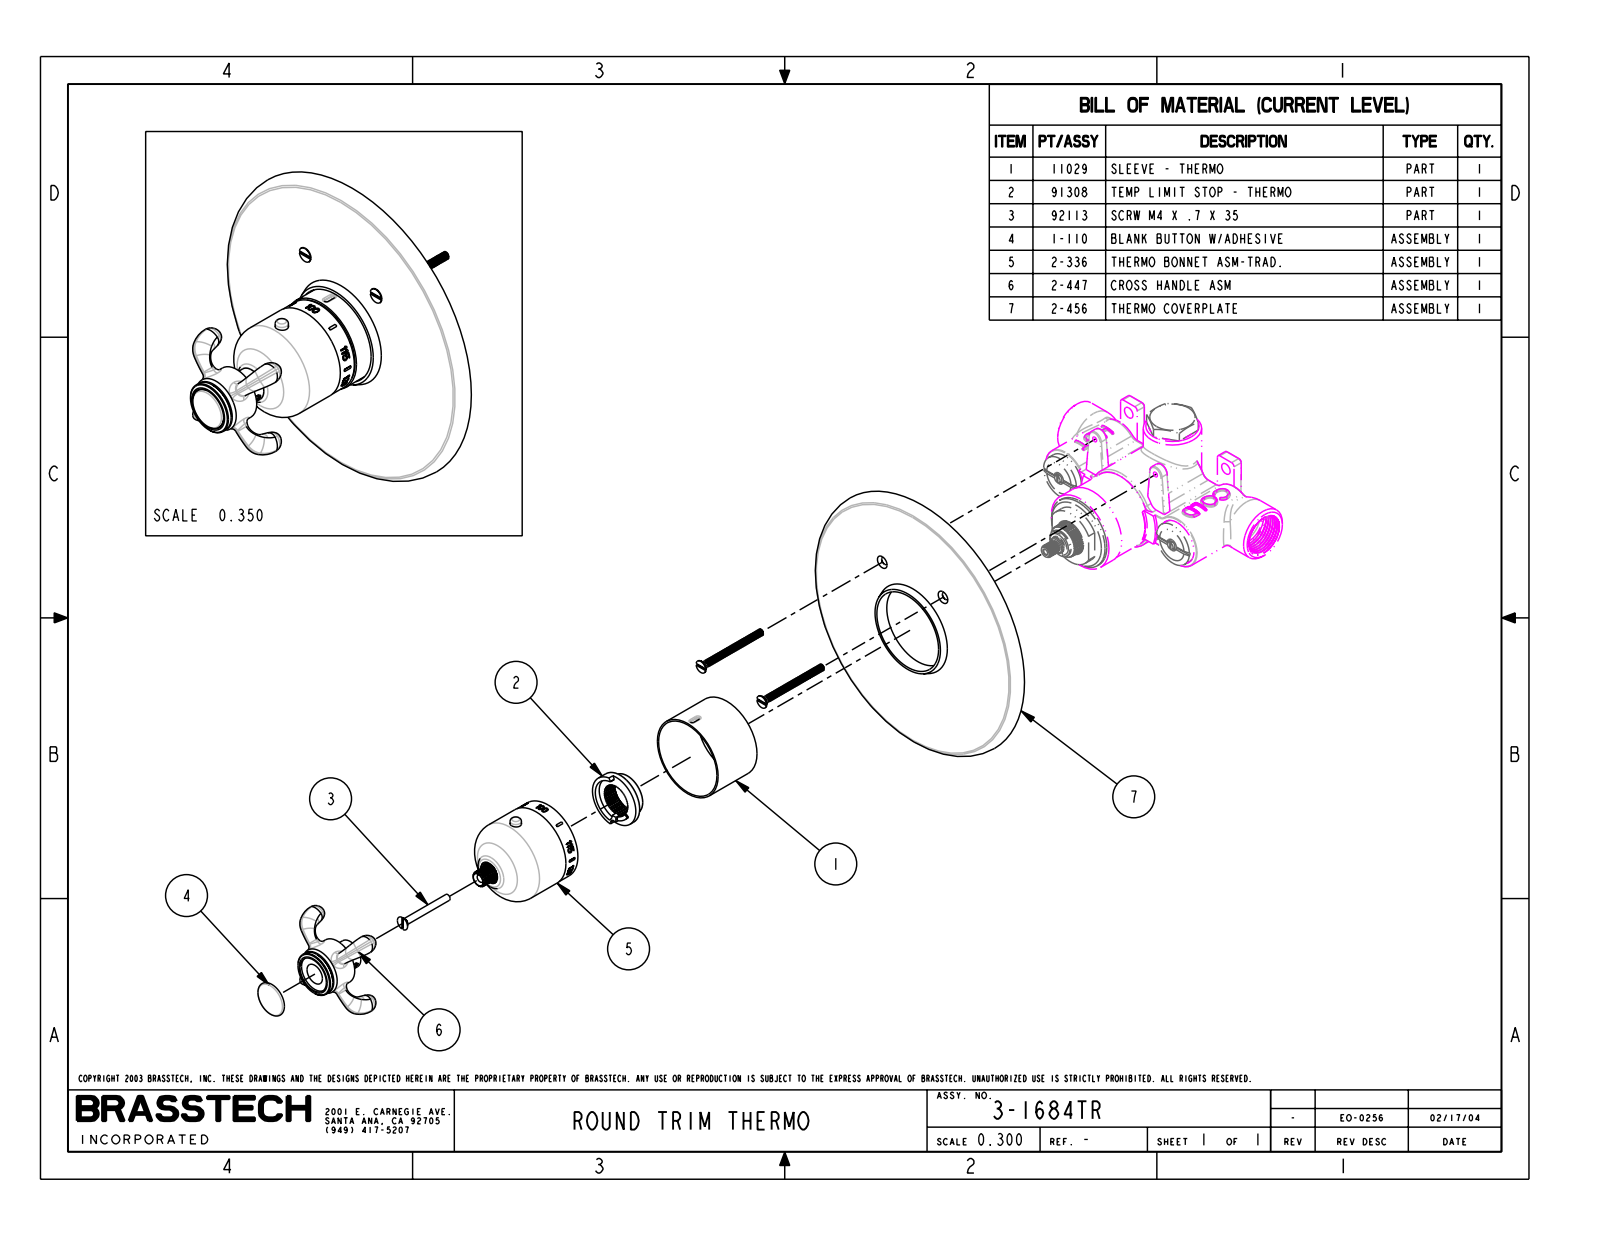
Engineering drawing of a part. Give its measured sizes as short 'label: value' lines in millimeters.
name: 11126_AF0; 91311; 92075_AF18; 92075_AF19 (+8 more)
written by: PRO/ENGINEER BY PARAMETRIC TECHNOLOGY CORPORATION, 2013150 (CONFIG_CONTROL_DESIGN)
unit: mm
bodies: 19 solids, 1950 faces (748 planar, 430 cylindrical, 772 other)
size: 168.3 × 168.3 × 113.7
volume: 94 140 mm³; area: 133 000 mm²
holes: 2× ⌀3.5, 1× ⌀0.7, 1× ⌀3, 1× ⌀4.8, 1× ⌀6.9, 1× ⌀6.9, 1× ⌀12.9, 1× ⌀21.7, 1× ⌀40, 1× ⌀43.1, 1× ⌀45, 1× ⌀48.3
bosses: 4× ⌀4.2, 2× ⌀7.9, 2× ⌀4, 2× ⌀3.3, 1× ⌀54.4, 1× ⌀50, 1× ⌀49.3, 1× ⌀49
rounds: 3× R4.7, 2× R1.9, 2× R2.2, 1× R0.5, 1× R1.4, 1× R2.8, 1× R3.5, 1× R4.2
face distances: 1.3, 51.7, 50.4, 6.7, 8, 58.3, 32.9, 26.3, 25, 25.4
hole spacings: 16.3, 23.6
